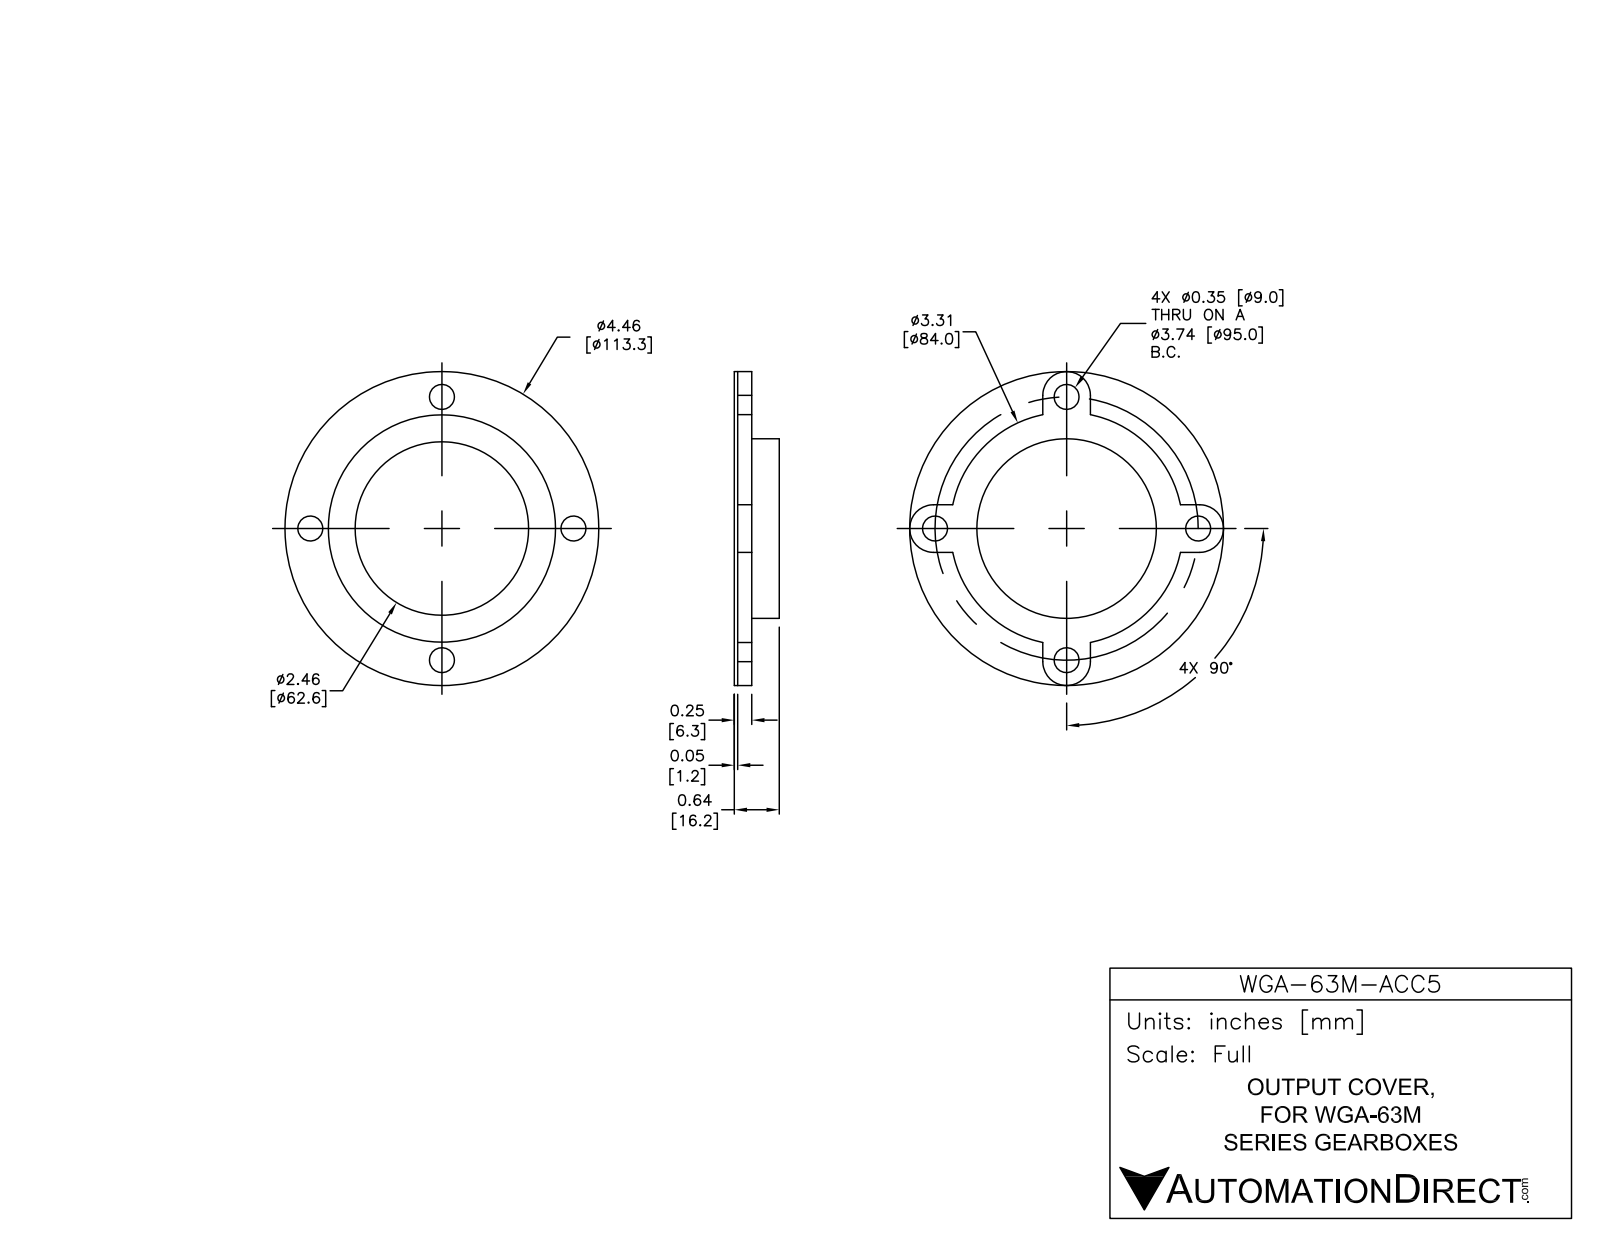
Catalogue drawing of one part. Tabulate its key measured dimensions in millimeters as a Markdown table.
| quantity | value |
| --- | --- |
| part name | WGA-63M-ACC5 |
| STEP written by | SolidWorks 2014 (AUTOMOTIVE_DESIGN) |
| units | millimeters |
| bodies | 1 solid, 42 faces (17 planar, 25 cylindrical, 0 other) |
| overall size | 113.3 × 113.3 × 16.2 |
| volume | 18 600 mm³ |
| surface area | 27 900 mm² |
| round holes (diameter × count) | 9 × 4, 62.6 × 1, 82 × 1 |
| round bosses / shafts (diameter × count) | 113.3 × 1, 64.8 × 1 |
| partial cylindrical surfaces (radius × count) | 8.6 × 4, 42 × 1 |
| main face-to-face distances | 1.2, 15, 9.9, 5.1, 16.2, 13.8, 8.7, 6.3, 11.1, 3.9 |
| hole center spacings | 47.5, 67.2, 95 |
